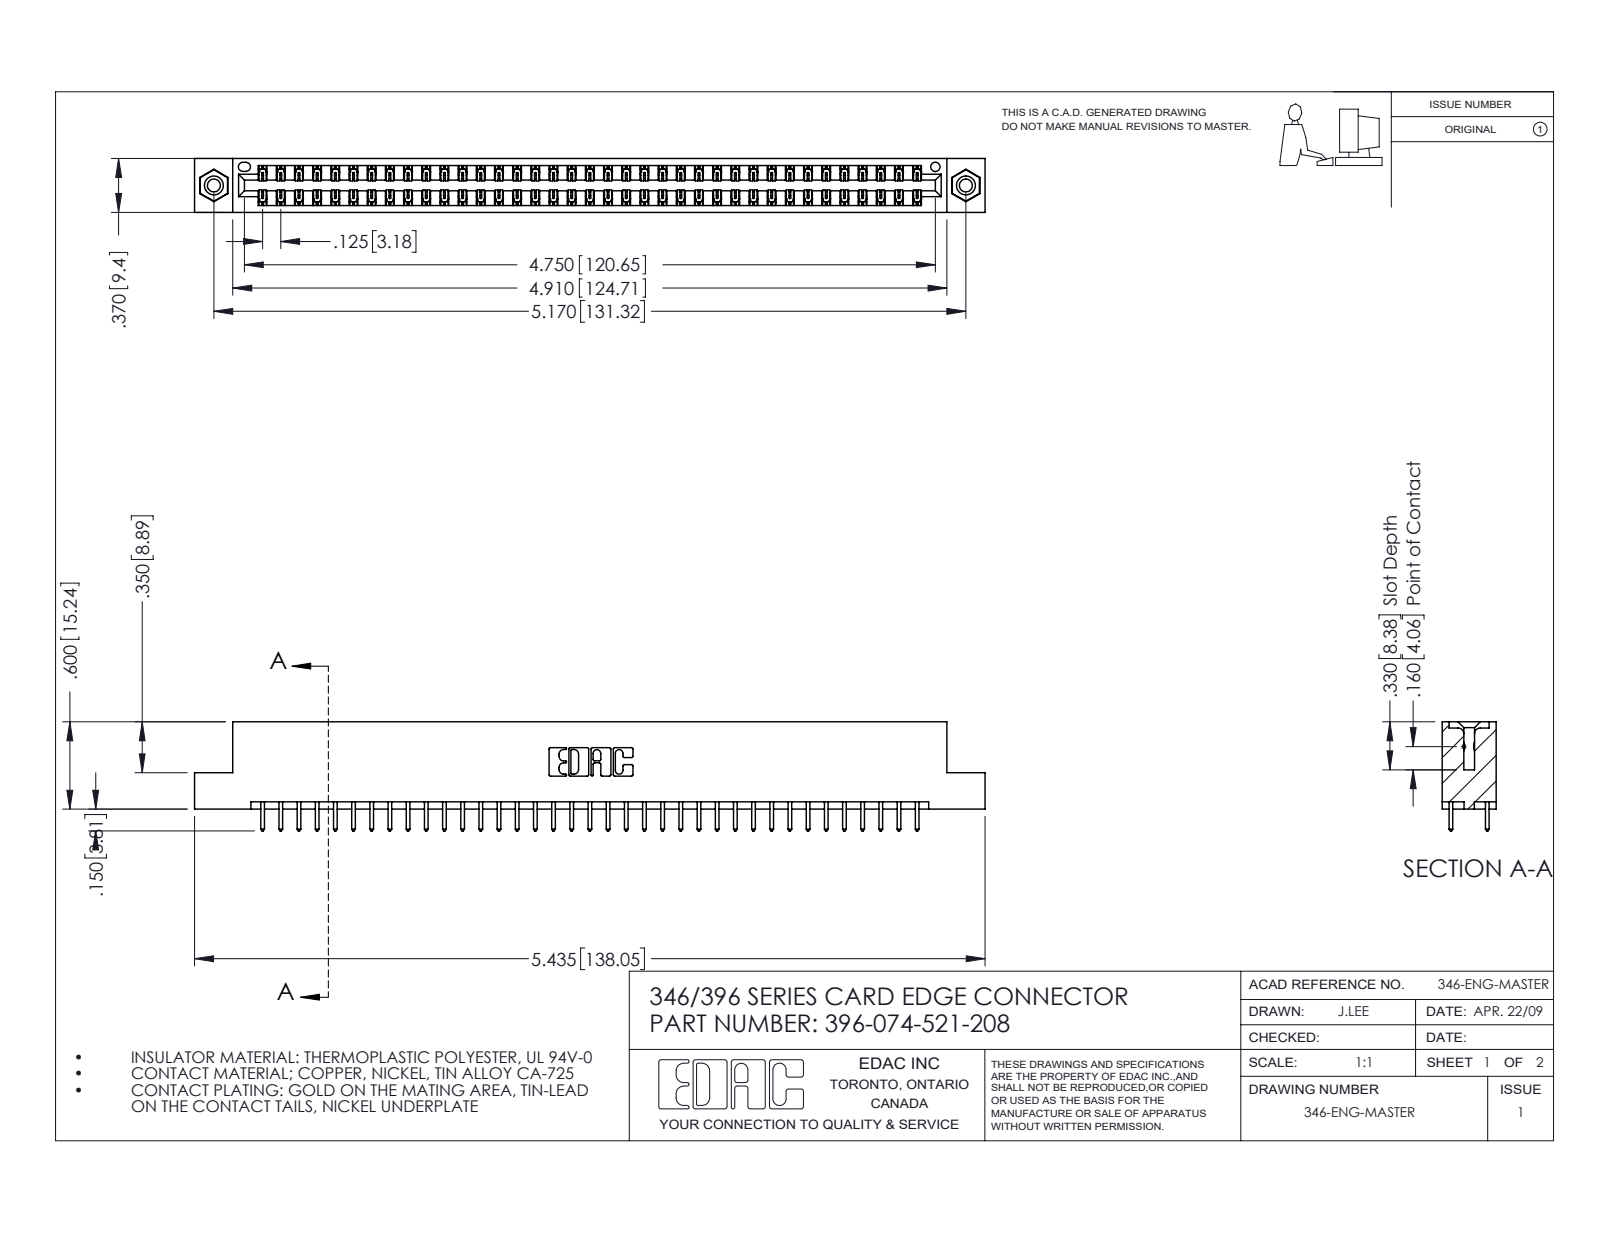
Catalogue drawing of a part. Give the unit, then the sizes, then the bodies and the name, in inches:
Units: inches
Overall size (bounding box): 5.435 × 0.75 × 0.37
Round holes (diameter × count): ⌀0.089 ×2, ⌀0.125 ×2, ⌀0.156 ×2, ⌀0.064 ×1
Round bosses / shafts (diameter × count): ⌀0.155 ×2
Partial cylindrical surfaces — rounded edges, fillets, slot ends (radius × count): R0.006 ×111, R0.01 ×74, R0.01 ×22, R0.007 ×6, R0.031 ×6, R0.026 ×3, R0.014 ×2, R0.022 ×2
Main face-to-face distances: 0.048, 0.322, 0.25, 0.37, 0.072, 0.298, 0.025, 0.275, 0.148, 0.222
Hole centre spacings: 0.246, 4.961, 5.17
Volume: 0.817 in³ · Surface area: 28.11 in²
Bodies: 77 solids, 4030 faces (2698 planar, 1316 cylindrical, 16 other)
Part name (STEP PRODUCT): 346 Part_Flush Mounting Lugs - 0.156 Dia-TI; 345-292-001_345-293-121; 396-074-521-208; 345-250-001_345-250-003-102
STEP written by: SolidWorks 2016 (CONFIG_CONTROL_DESIGN)
